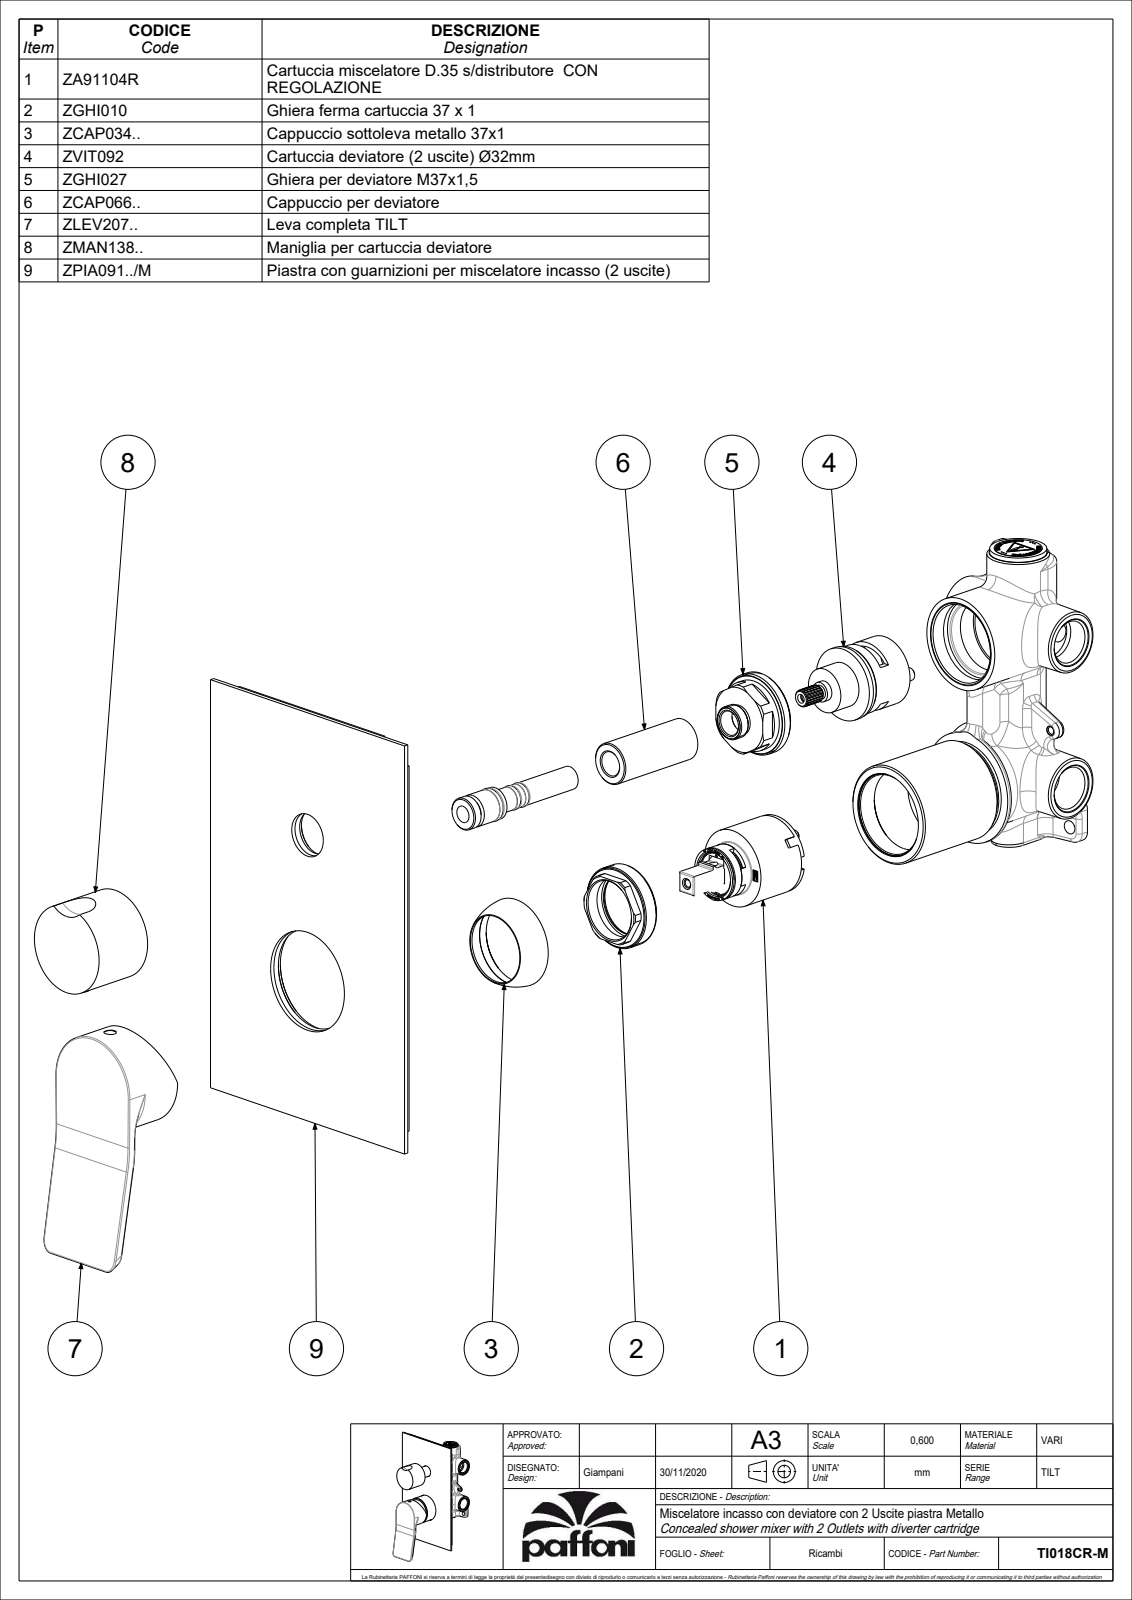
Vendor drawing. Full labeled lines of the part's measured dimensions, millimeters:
Part name (STEP PRODUCT): TI018CR-M
STEP written by: CREO PARAMETRIC BY PTC INC, 2020044 (CONFIG_CONTROL_DESIGN)
Units: millimetres
Bodies: 2 solids, 217 faces (72 planar, 83 cylindrical, 62 other)
Overall size (bounding box): 204.58 × 120 × 64.05
Volume: 114 390 mm³ · Surface area: 85 424 mm²
Round holes (diameter × count): ⌀3 ×2, ⌀4.2 ×2, ⌀36 ×2, ⌀3.2 ×1, ⌀5.5 ×1, ⌀11 ×1, ⌀14.8 ×1, ⌀30.6 ×1, ⌀37.5 ×1
Round bosses / shafts (diameter × count): ⌀7.6 ×2, ⌀45.5 ×1, ⌀44.8 ×1, ⌀40 ×1, ⌀24 ×1, ⌀18.7 ×1, ⌀5.5 ×1
Partial cylindrical surfaces — rounded edges, fillets, slot ends (radius × count): R0.5 ×10, R1.5 ×2, R5 ×2, R12.5 ×1, R44.14 ×1, R63 ×1
Main face-to-face distances: 2, 4.02, 55.1, 53.1, 4, 51.1, 49.1, 23.9, 25.9, 25.2
Hole centre spacings: 1.8, 10, 68, 78
